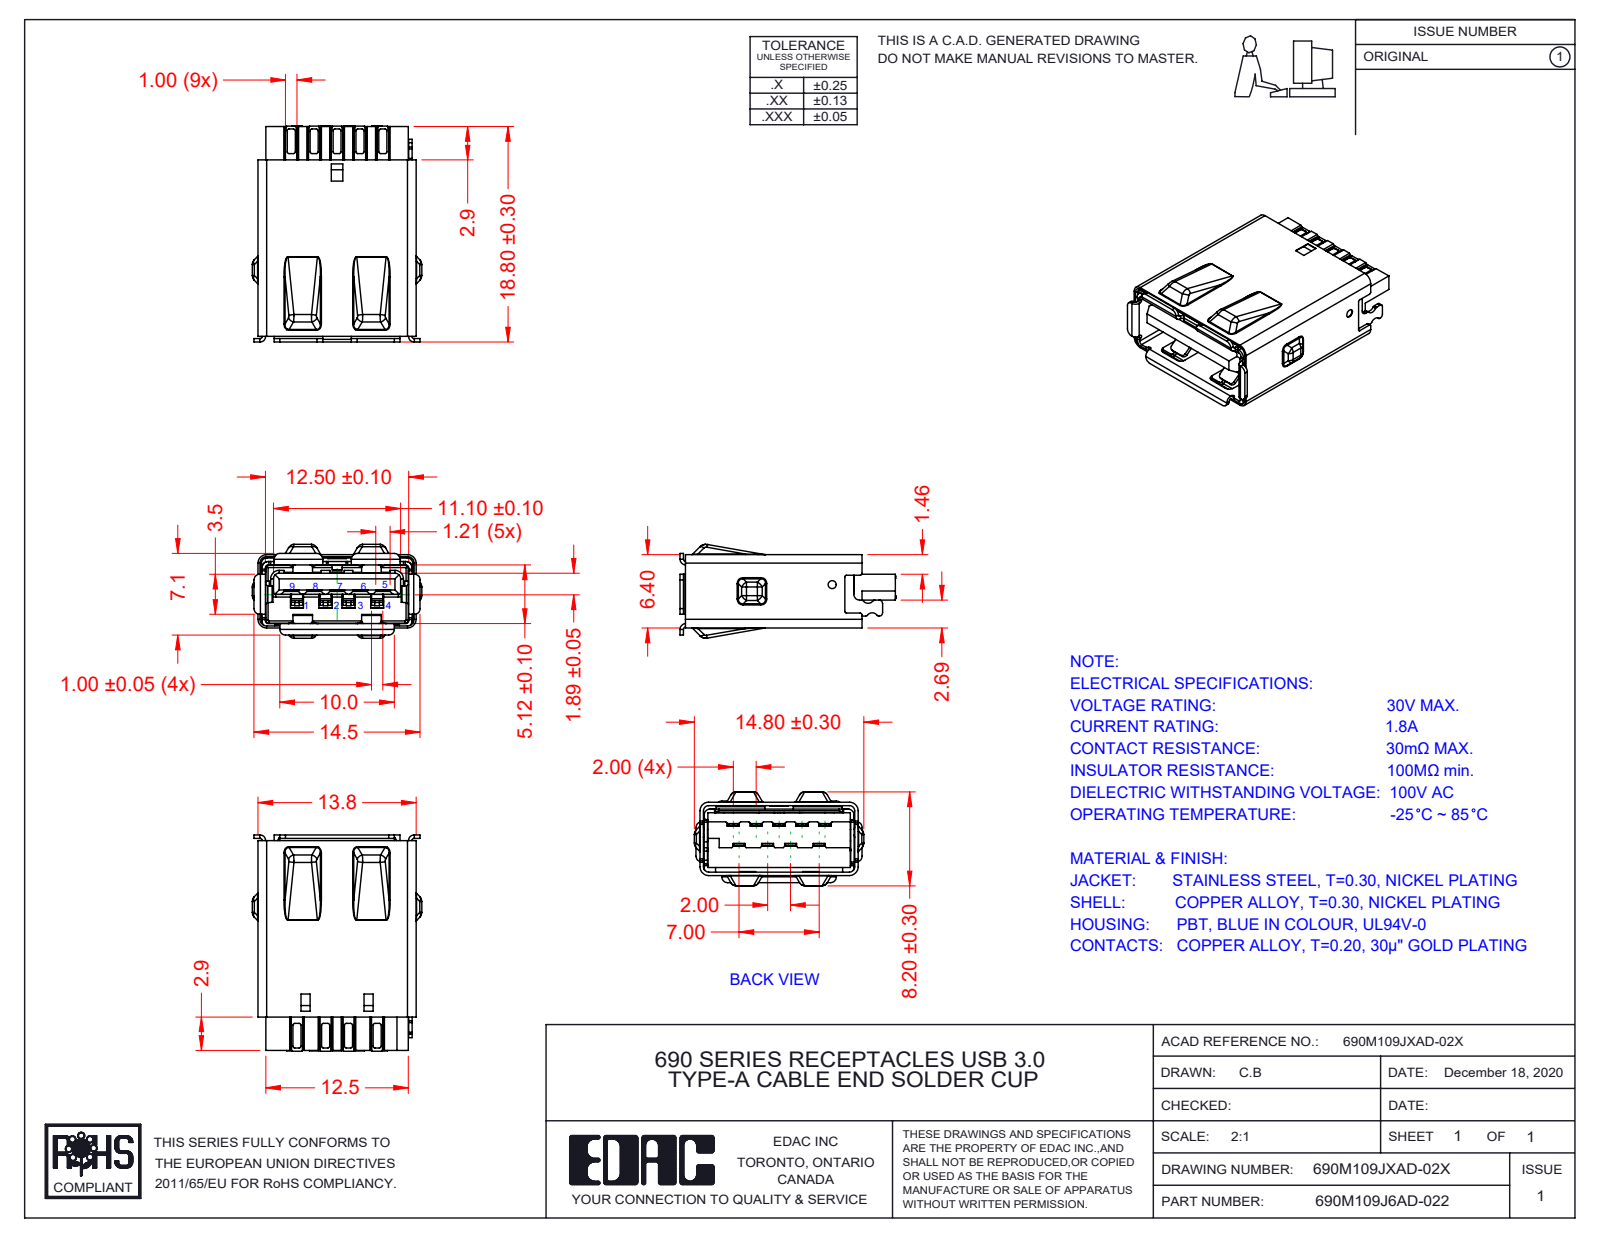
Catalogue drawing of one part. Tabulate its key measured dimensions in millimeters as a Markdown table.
| quantity | value |
| --- | --- |
| part name | 690M109J1AD-022; Insulator2 690M109JXAD-02X_Blue; Contact3 690M109JXAD-02X; Insulator1 690M109JXAD-02X_Blue (+6 more) |
| STEP written by | SolidWorks 2020 (AUTOMOTIVE_DESIGN) |
| units | millimeters |
| bodies | 13 solids, 2416 faces (1451 planar, 775 cylindrical, 190 other) |
| overall size | 18.86 × 14.8 × 8.2 |
| volume | 811 mm³ |
| surface area | 3 982 mm² |
| round holes (diameter × count) | 0.7 × 1 |
| partial cylindrical surfaces (radius × count) | 0.15 × 140, 0.2 × 68, 0.1 × 58, 0.5 × 42, 0.3 × 32, 0.13 × 30, 0.25 × 20, 0.6 × 19 |
| main face-to-face distances | 5.5, 5.8, 6.1, 0.6, 0.35, 5.42, 5.72, 6.02, 13.15, 0.38 |
